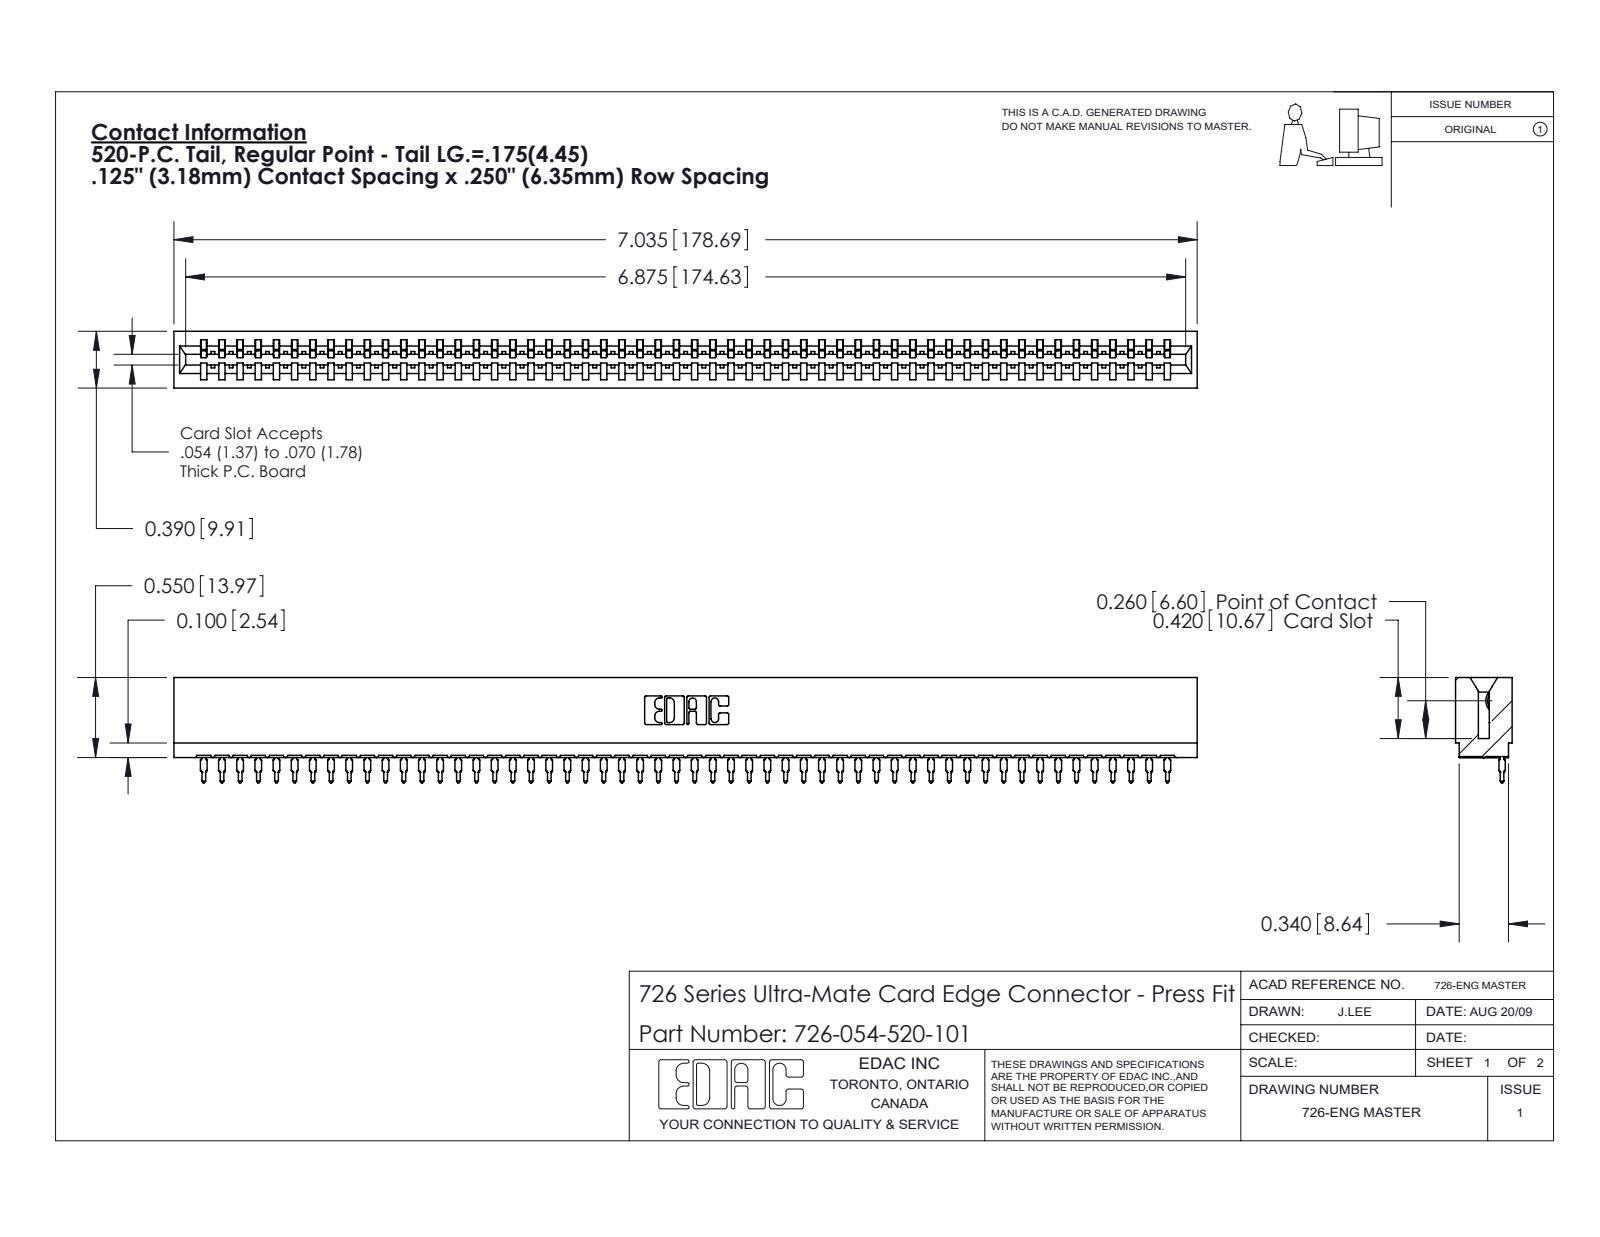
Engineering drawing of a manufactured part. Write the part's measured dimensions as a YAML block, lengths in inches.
part_name: "726-054-520-101; 726 Part_.515 Slot Depth - 01; 746-292-001_520"
step_written_by: "SolidWorks 2020 (CONFIG_CONTROL_DESIGN)"
units: inches
bodies: {solids: 55, faces: 5929, planar: 3457, cylindrical: 1068, other: 1404}
overall_size: [7.035, 0.724, 0.39]
volume: 0.965
surface_area: 37.08
partial_cylinders:
  - {radius: 0.021, count: 108}
  - {radius: 0.015, count: 55}
  - {radius: 0.01, count: 22}
  - {radius: 0.007, count: 6}
  - {radius: 0.031, count: 6}
  - {radius: 0.005, count: 4}
  - {radius: 0.011, count: 4}
  - {radius: 0.026, count: 3}
face_to_face_distances: [0.057, 0.333, 0.39, 0.025, 0.307, 0.275, 0.25, 0.365, 0.032, 0.174]
